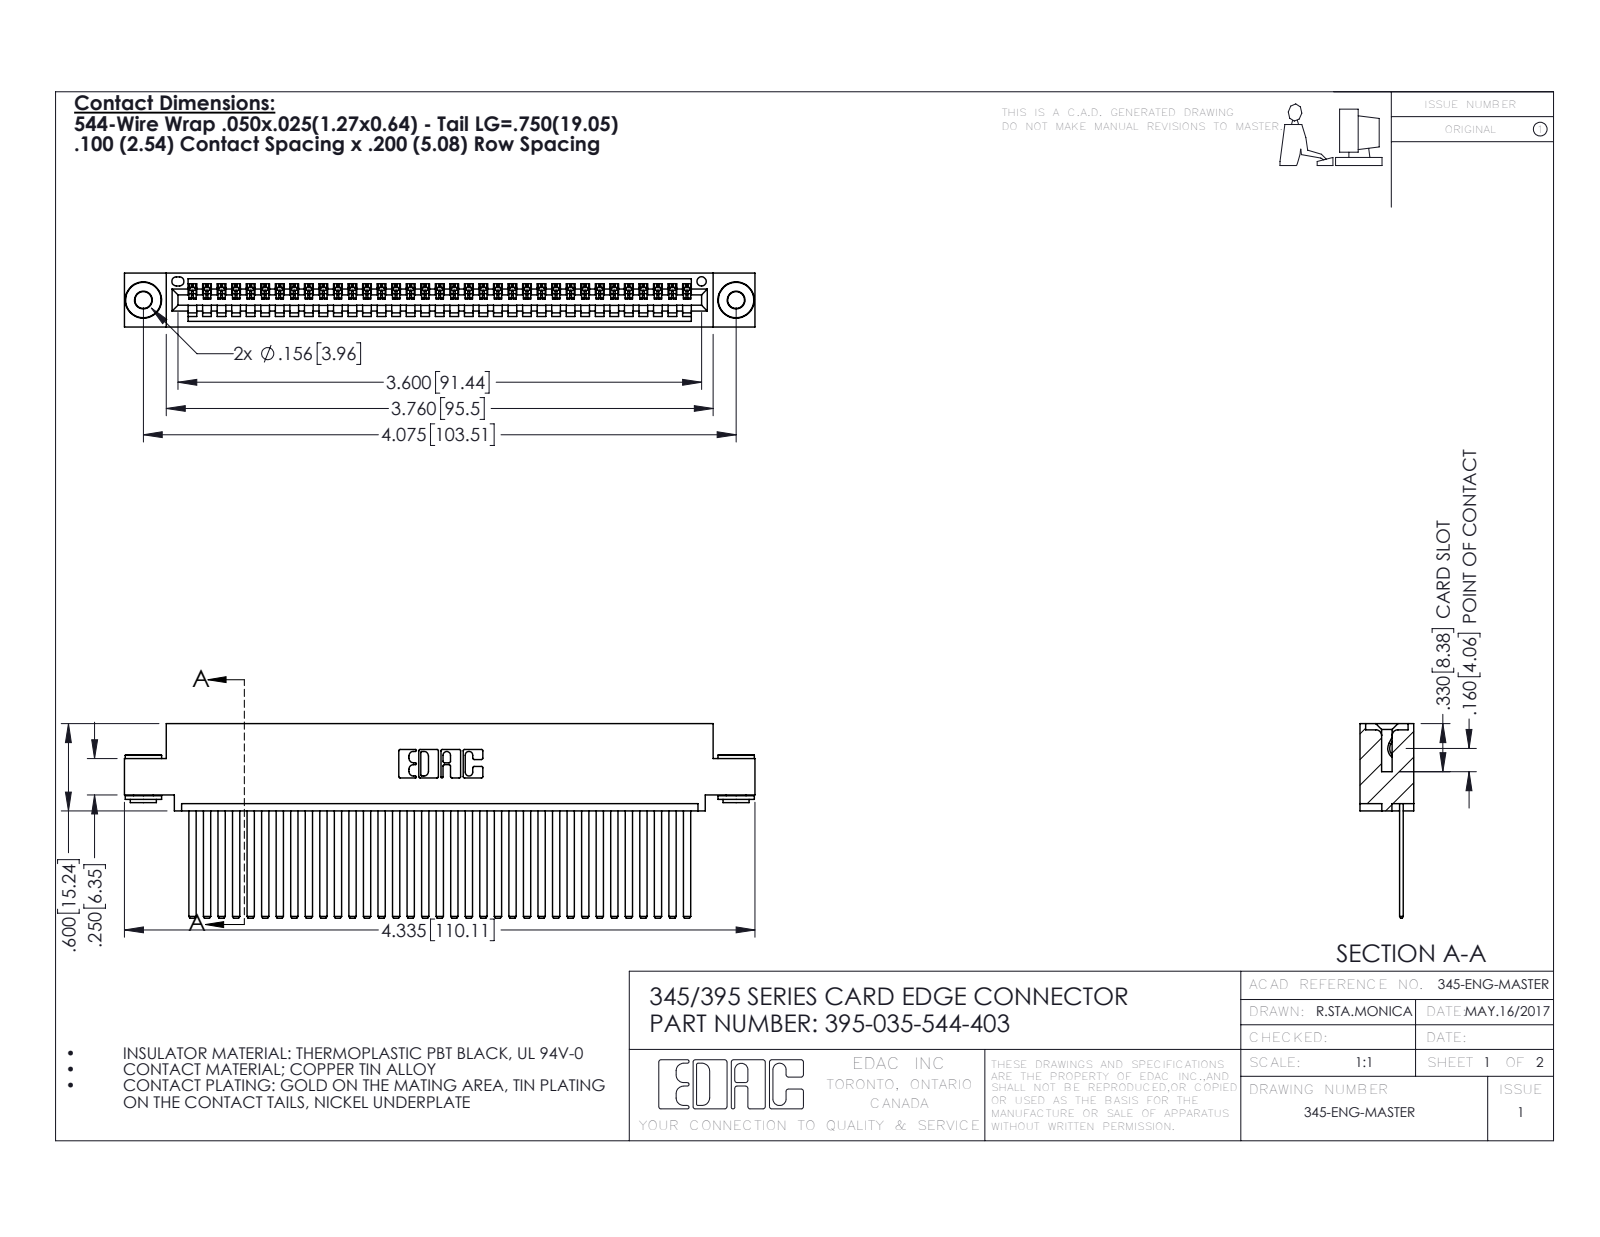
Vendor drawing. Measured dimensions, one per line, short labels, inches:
name: 345-292-001_345-293-144; 345 Part_0.110 Offset - 0.156 Dia-TH; 345-250-002_345-250-002-102; 395-035-544-403
written by: SolidWorks 2016 (CONFIG_CONTROL_DESIGN)
unit: in
bodies: 38 solids, 1988 faces (1354 planar, 626 cylindrical, 8 other)
size: 4.335 × 1.337 × 0.37
volume: 0.656 in³; area: 24.35 in²
holes: 2× ⌀0.116, 2× ⌀0.156, 1× ⌀0.064
bosses: 2× ⌀0.25, 2× ⌀0.18, 2× ⌀0.136
rounds: 70× R0.006, 22× R0.01, 6× R0.007, 6× R0.031, 3× R0.026, 2× R0.031, 2× R0.04, 1× R0.014
face distances: 0.072, 0.298, 0.025, 0.098, 0.272, 0.37, 0.2, 0.225, 0.149, 0.072
hole spacings: 0.27, 3.839, 4.075
